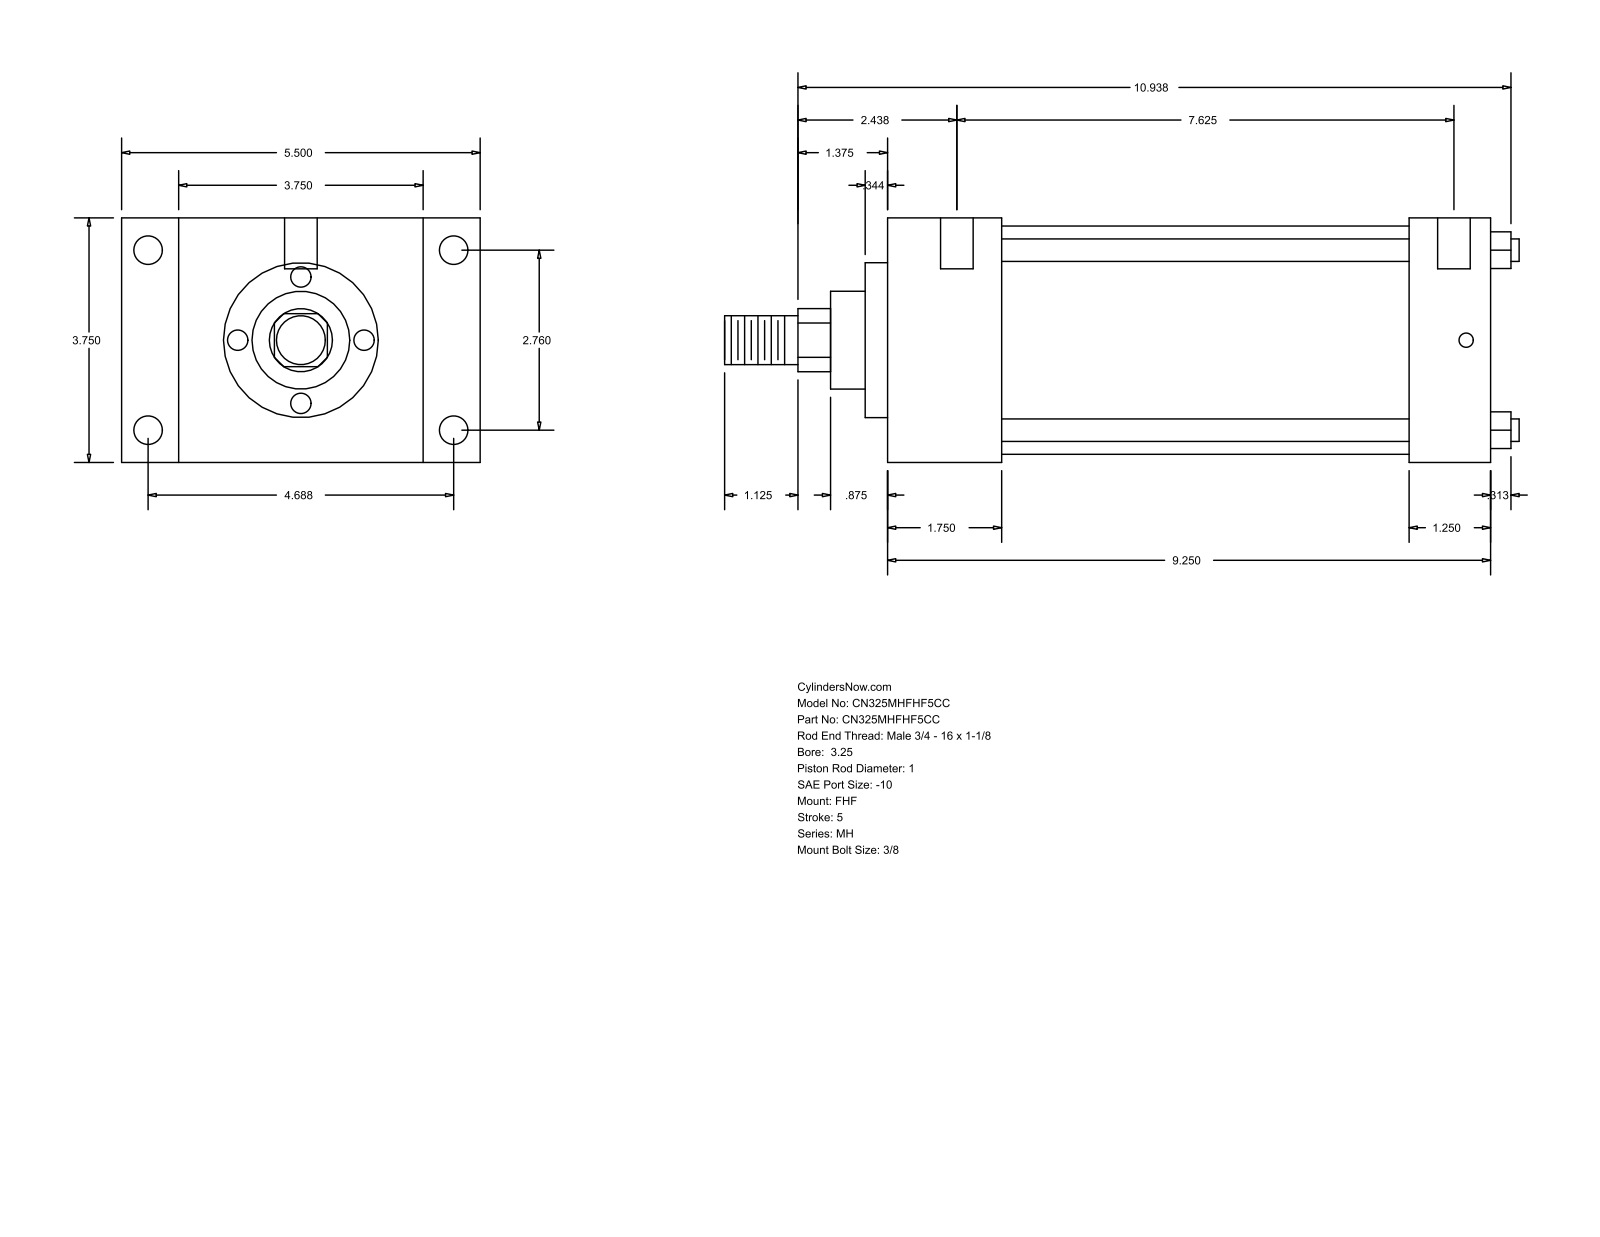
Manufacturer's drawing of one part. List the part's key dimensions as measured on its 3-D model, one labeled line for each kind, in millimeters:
Part name (STEP PRODUCT): MH_FHF__0325_1
STEP written by: GSSL Pune (CONFIG_CONTROL_DESIGN)
Units: millimetres
Bodies: 0 solids, 90 faces (61 planar, 29 cylindrical, 0 other)
Overall size (bounding box): 309.56 × 139.7 × 95.25
Round holes (diameter × count): ⌀5.56 ×4, ⌀11.13 ×4, ⌀12.7 ×2
Round bosses / shafts (diameter × count): ⌀8.76 ×4, ⌀88.9 ×1, ⌀60.33 ×1, ⌀38.1 ×1, ⌀25.4 ×1, ⌀19.05 ×1
Partial cylindrical surfaces — rounded edges, fillets, slot ends (radius × count): R12.29 ×1
Main face-to-face distances: 95.24, 234.96, 44.46, 190.5, 22.23, 117.47, 139.7, 203.2, 158.74, 31.76
Hole centre spacings: 70.1, 119.06, 138.16, 200.02, 1.58, 4.76, 193.68, 195.26
